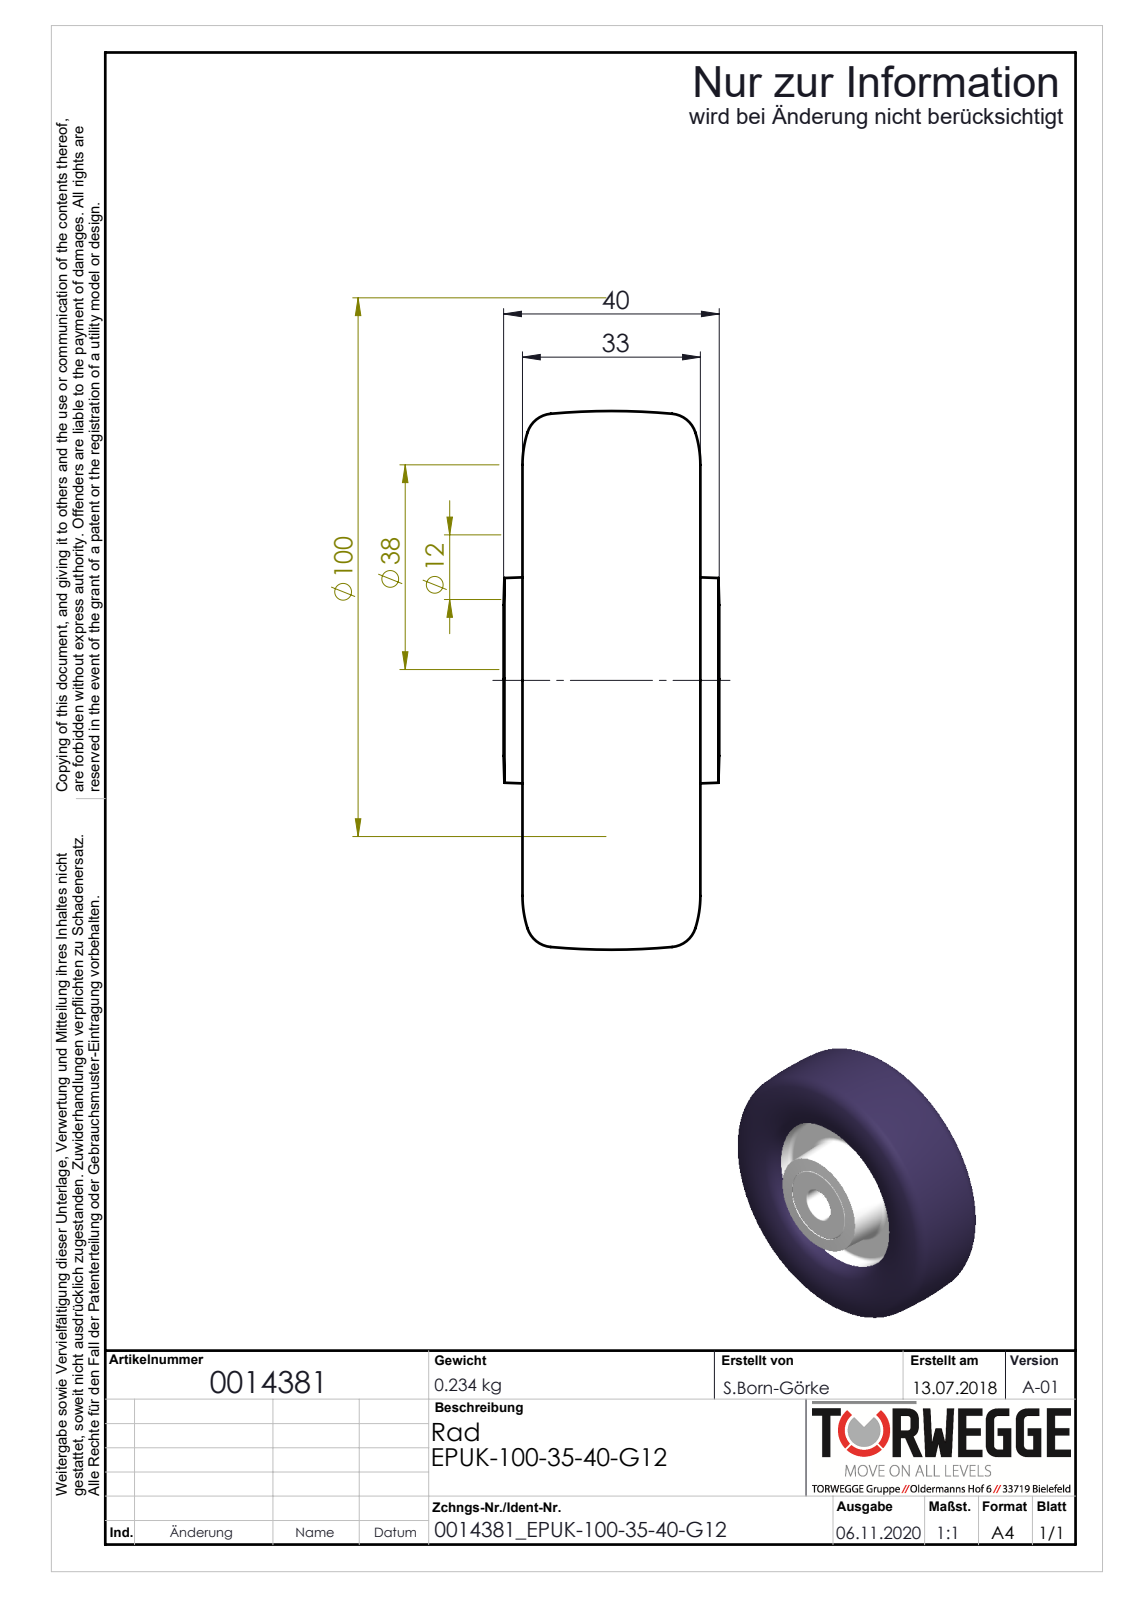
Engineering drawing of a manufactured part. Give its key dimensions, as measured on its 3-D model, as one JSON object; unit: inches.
{"part_name": "0014381", "step_written_by": "SolidWorks 2018 (AUTOMOTIVE_DESIGN)", "units": "inches", "bodies": {"solids": 3, "faces": 188, "planar": 40, "cylindrical": 22, "other": 126}, "overall_size": [3.937, 3.937, 1.575], "volume_in3": 12.57, "surface_area_in2": 58.24, "round_holes": [[0.472, 1], [0.906, 1], [2.328, 1]], "round_bosses_or_shafts": [[1.102, 1]], "partial_cylinders_radius": [[1.555, 1]], "face_to_face_distances": [0.276, 0.669, 0.394, 0.315, 0.591, 0.984, 1.26, 0.945, 1.575, 0.374]}
